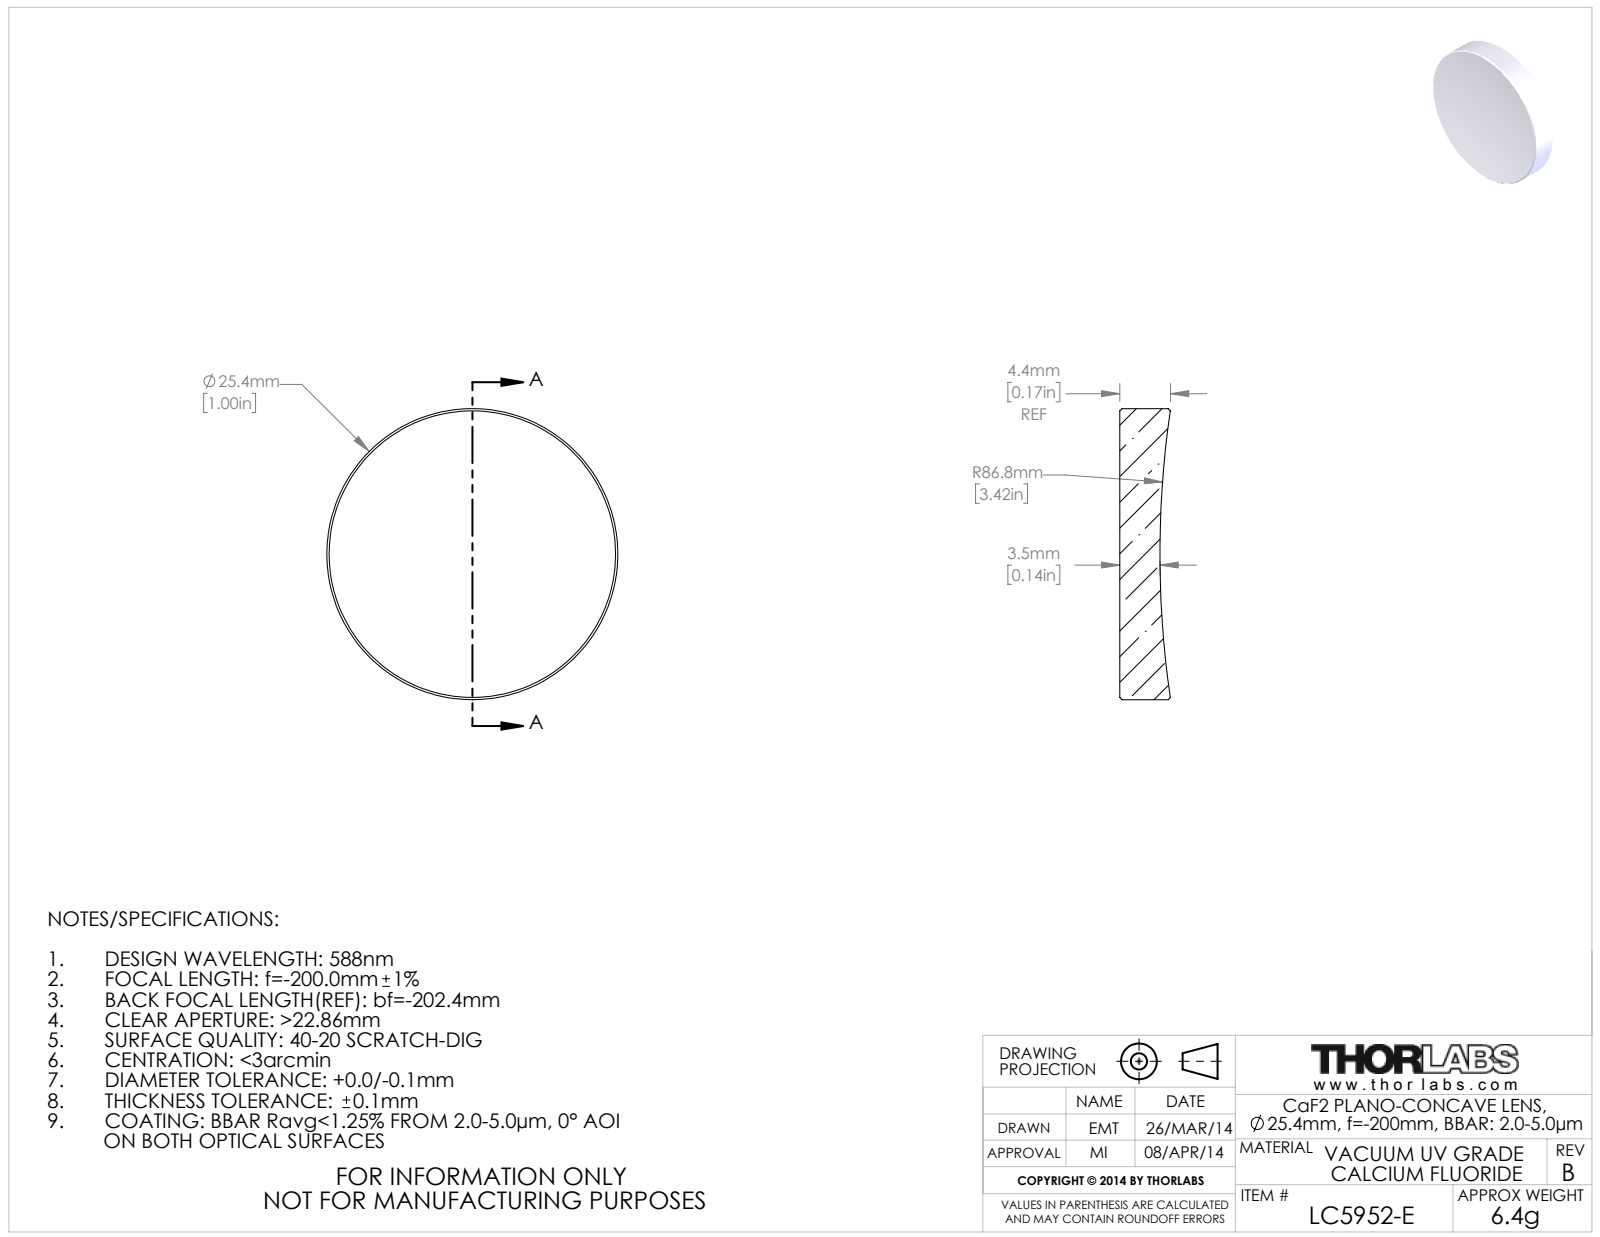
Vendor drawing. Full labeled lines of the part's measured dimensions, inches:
Part name (STEP PRODUCT): 20146-E0W
STEP written by: SolidWorks 2016 (CONFIG_CONTROL_DESIGN)
Units: inches
Bodies: 1 solid, 9 faces (1 planar, 2 cylindrical, 6 other)
Overall size (bounding box): 1 × 1 × 0.173
Volume: 0.122 in³ · Surface area: 2.092 in²
Round bosses / shafts (diameter × count): ⌀1 ×1
